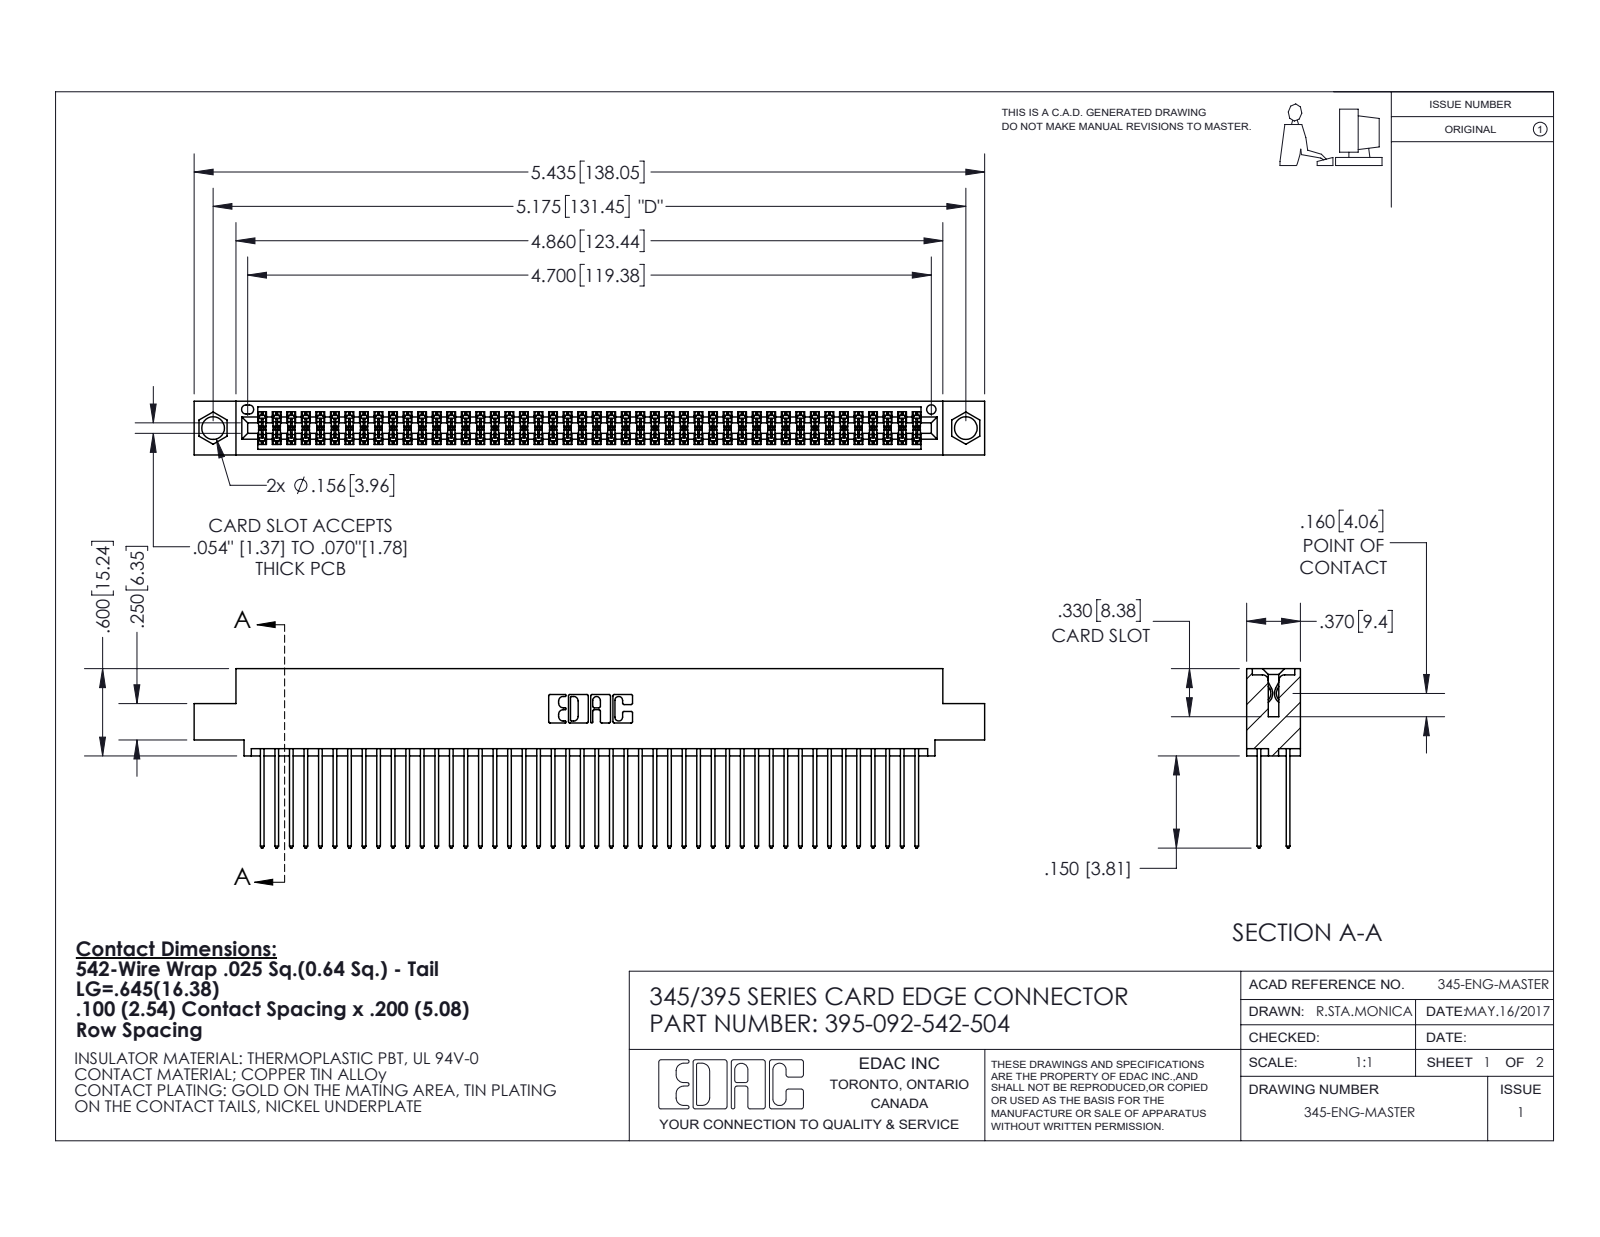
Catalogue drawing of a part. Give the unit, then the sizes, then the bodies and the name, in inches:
Units: inches
Overall size (bounding box): 5.435 × 1.232 × 0.37
Round holes (diameter × count): ⌀0.156 ×2, ⌀0.064 ×1
Partial cylindrical surfaces — rounded edges, fillets, slot ends (radius × count): R0.006 ×138, R0.01 ×92, R0.01 ×22, R0.007 ×6, R0.031 ×6, R0.026 ×3, R0.014 ×2, R0.019 ×2
Main face-to-face distances: 0.298, 0.072, 0.2, 0.098, 0.272, 0.025, 0.225, 0.37, 0.175, 0.149
Hole centre spacings: 0.27, 4.939, 5.175
Volume: 0.836 in³ · Surface area: 34.52 in²
Bodies: 93 solids, 4744 faces (3134 planar, 1610 cylindrical, 0 other)
Part name (STEP PRODUCT): 345 Part_0.110 Offset - 0.156 Dia-TI; 395-092-542-504; 345-292-001_345-293-142
STEP written by: SolidWorks 2020 (CONFIG_CONTROL_DESIGN)
